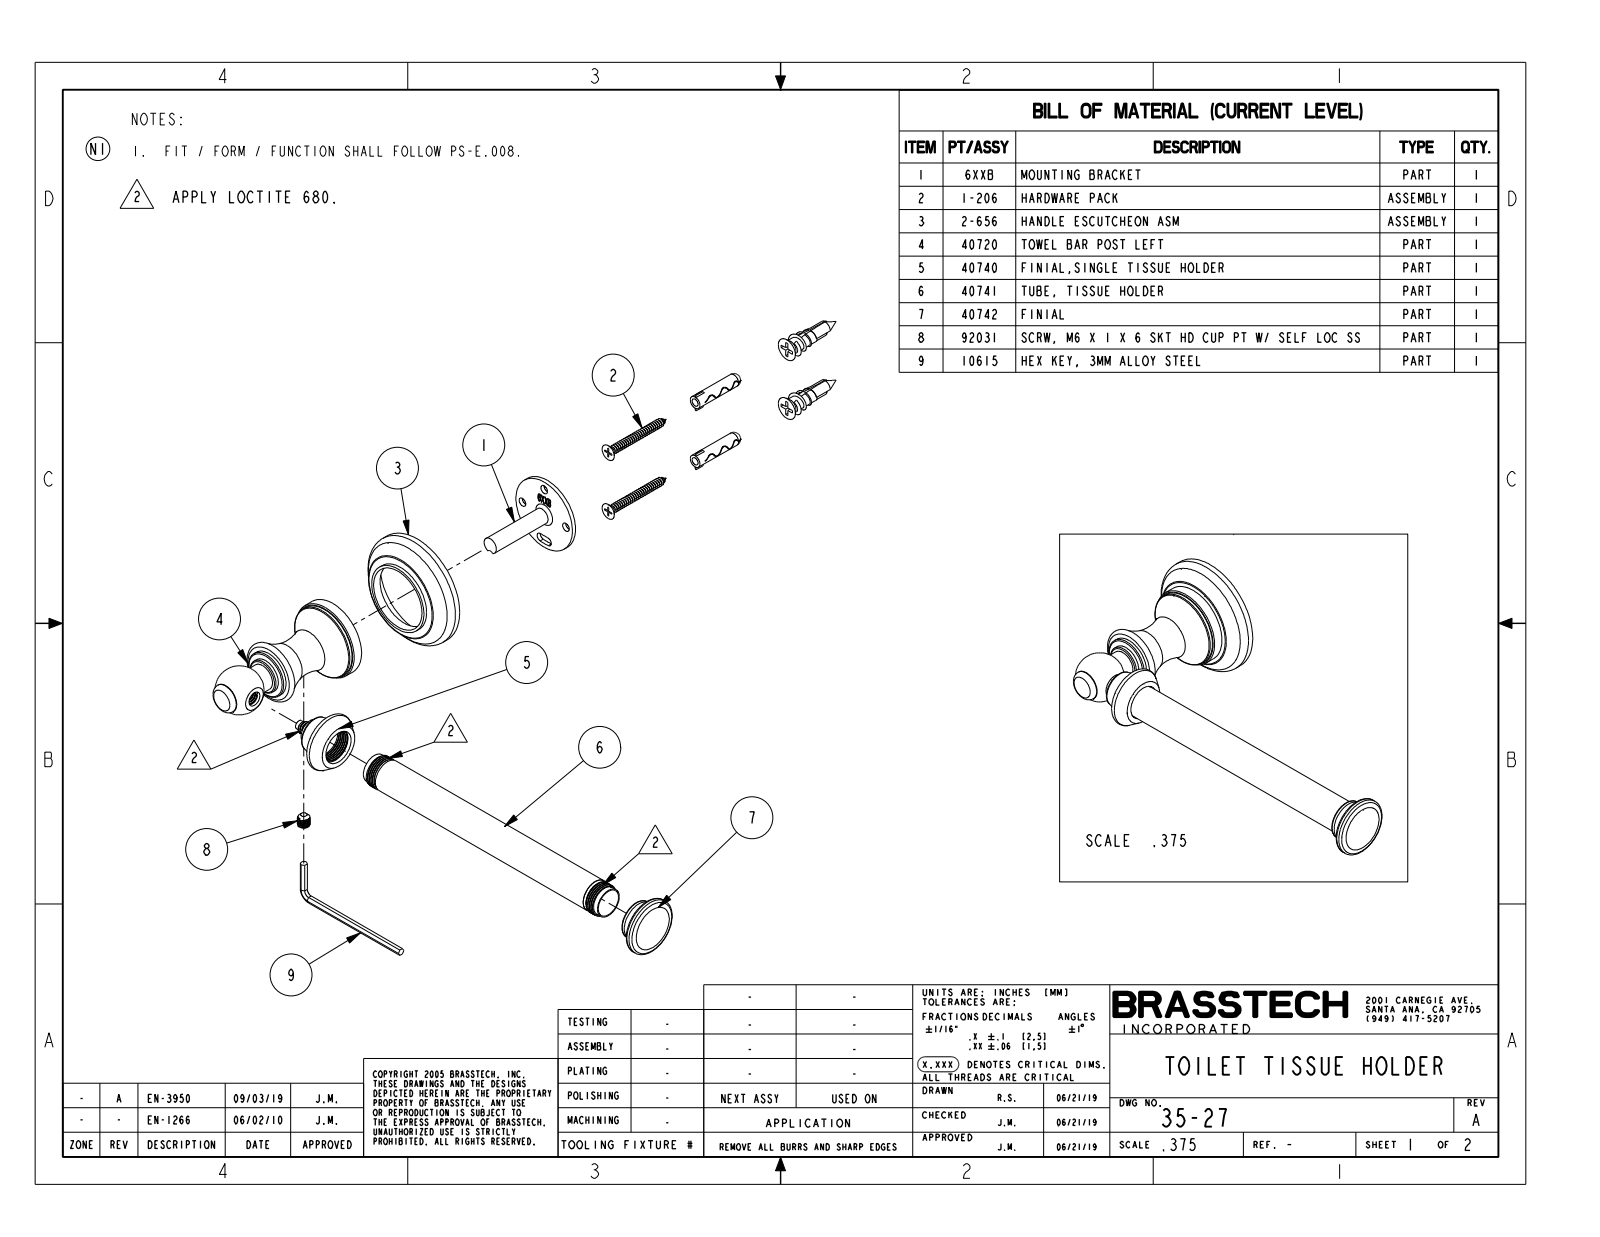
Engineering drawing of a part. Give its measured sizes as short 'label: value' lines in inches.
name: 35-27
written by: CREO PARAMETRIC BY PTC INC, 2018400 (AUTOMOTIVE_DESIGN)
unit: in
bodies: 1 solid, 115 faces (19 planar, 40 cylindrical, 56 other)
size: 7.989 × 3.422 × 2.2
volume: 5.597 in³; area: 36.09 in²
holes: 1× ⌀0.585, 1× ⌀0.65
bosses: 1× ⌀2.2, 1× ⌀1.49, 1× ⌀1.42, 1× ⌀1.35, 1× ⌀1.1, 1× ⌀0.9, 1× ⌀0.75, 1× ⌀0.66
face distances: 0.43, 0.08, 0.442, 0.012, 5.64, 2.102, 1.672, 1.66, 0.025, 6.085
